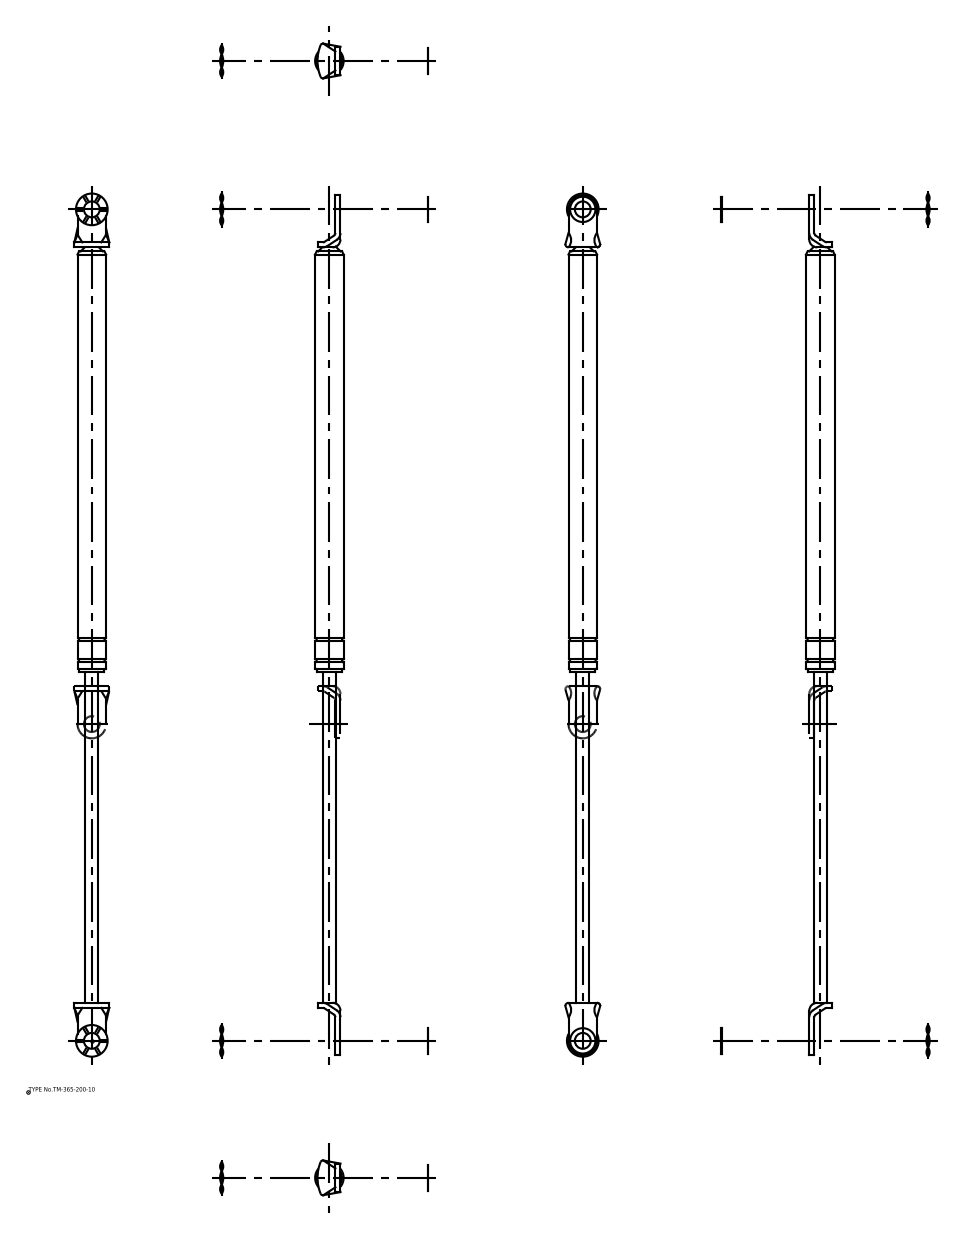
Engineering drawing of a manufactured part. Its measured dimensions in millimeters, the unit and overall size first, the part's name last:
Units: millimetres
Overall size (bounding box): 545 × 22 × 18.5
Round holes (diameter × count): ⌀10 ×2
Round bosses / shafts (diameter × count): ⌀16 ×3, ⌀20 ×2, ⌀18.5 ×1, ⌀18 ×1, ⌀8 ×1
Partial cylindrical surfaces — rounded edges, fillets, slot ends (radius × count): R4.4 ×2, R5 ×2, R9 ×2, R26.32 ×1
Main face-to-face distances: 3.2, 2, 5.2, 480.2, 3.7, 5.7, 0.5, 271.2, 212.2, 483.4
Hole centre spacings: 525
Volume: 83 685 mm³ · Surface area: 26 421 mm²
Bodies: 6 solids, 94 faces (42 planar, 44 cylindrical, 8 other)
Part name (STEP PRODUCT): ウェーブワッシャー; ワッシャー; 本体; 本体_div
STEP written by: spGate 16.7.1 (AUTOMOTIVE_DESIGN)
